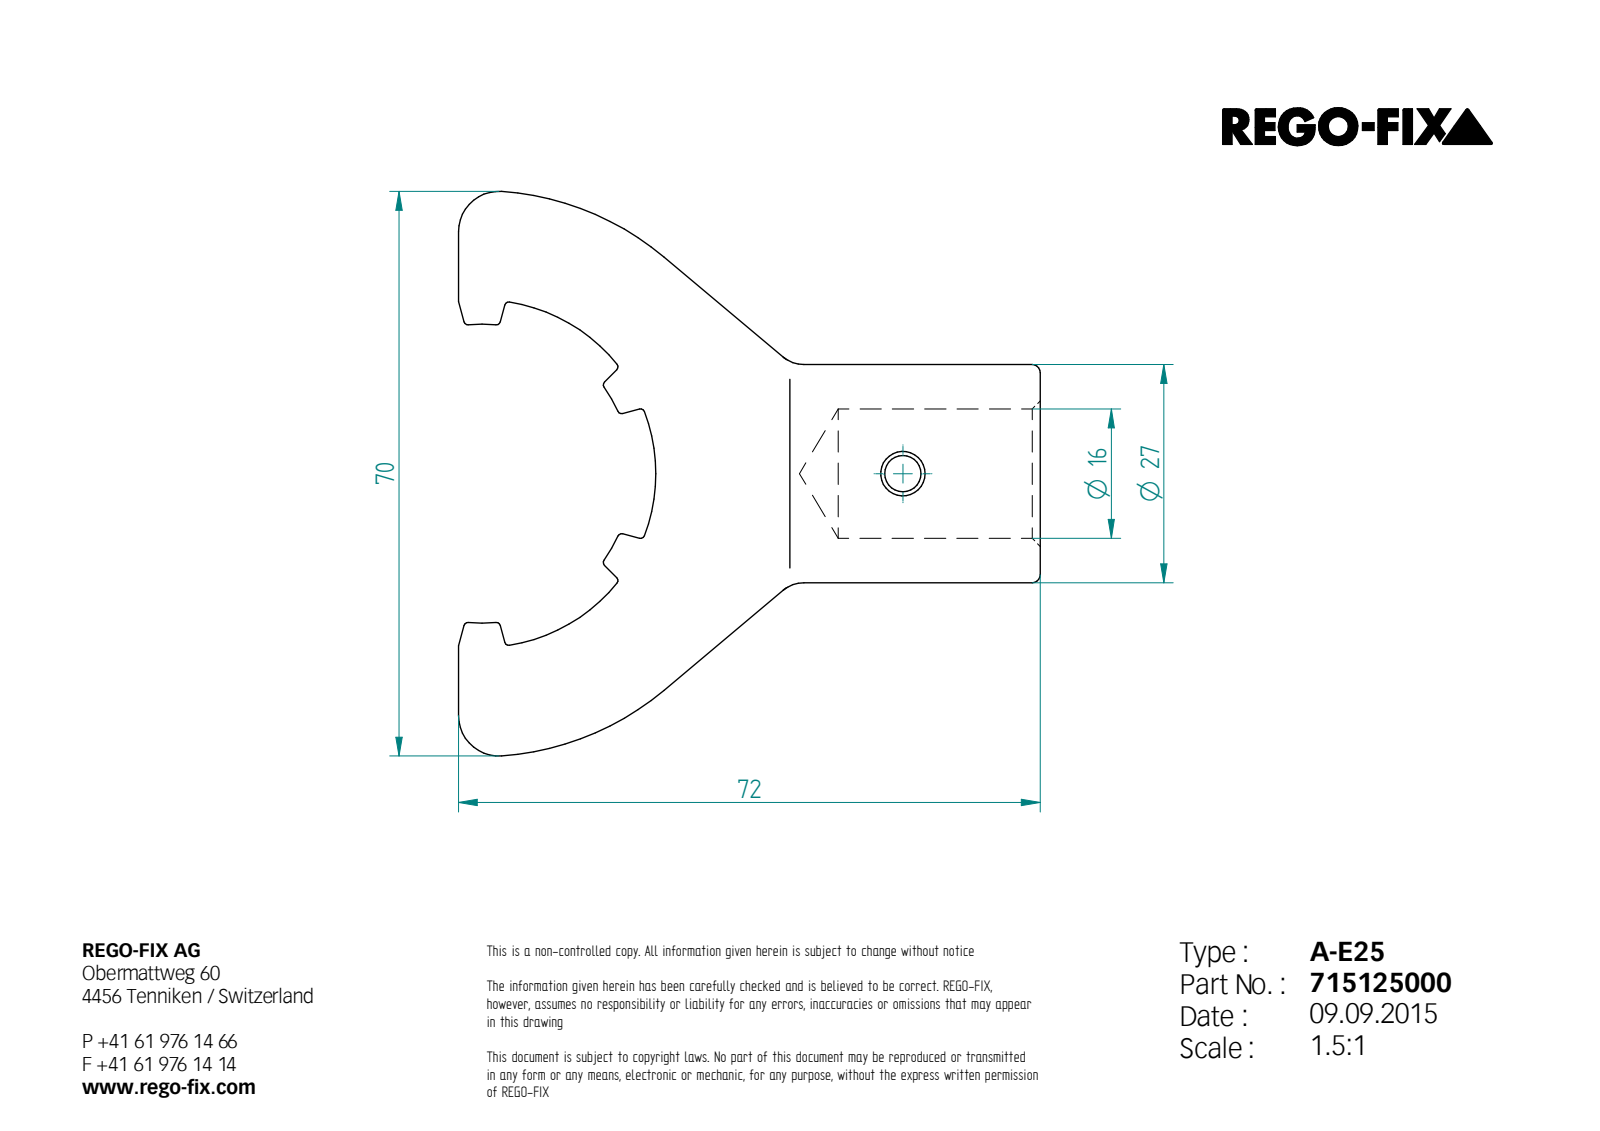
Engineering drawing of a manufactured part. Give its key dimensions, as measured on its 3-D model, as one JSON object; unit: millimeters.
{"step_written_by": "Unknown (AUTOMOTIVE_DESIGN)", "units": "millimeters", "bodies": {"solids": 1, "faces": 93, "planar": 17, "cylindrical": 44, "other": 32}, "overall_size": [72, 69.86, 27], "volume_mm3": 21024, "surface_area_mm2": 9012, "round_holes": [[4.5, 1], [5.5, 1], [16, 1]], "round_bosses_or_shafts": [[27, 1]], "partial_cylinders_radius": [[0.5, 14], [0.99, 6], [1.5, 6], [5, 2], [18.5, 1], [21.5, 1], [35, 1]], "face_to_face_distances": [6, 31, 41, 72, 5.38]}
